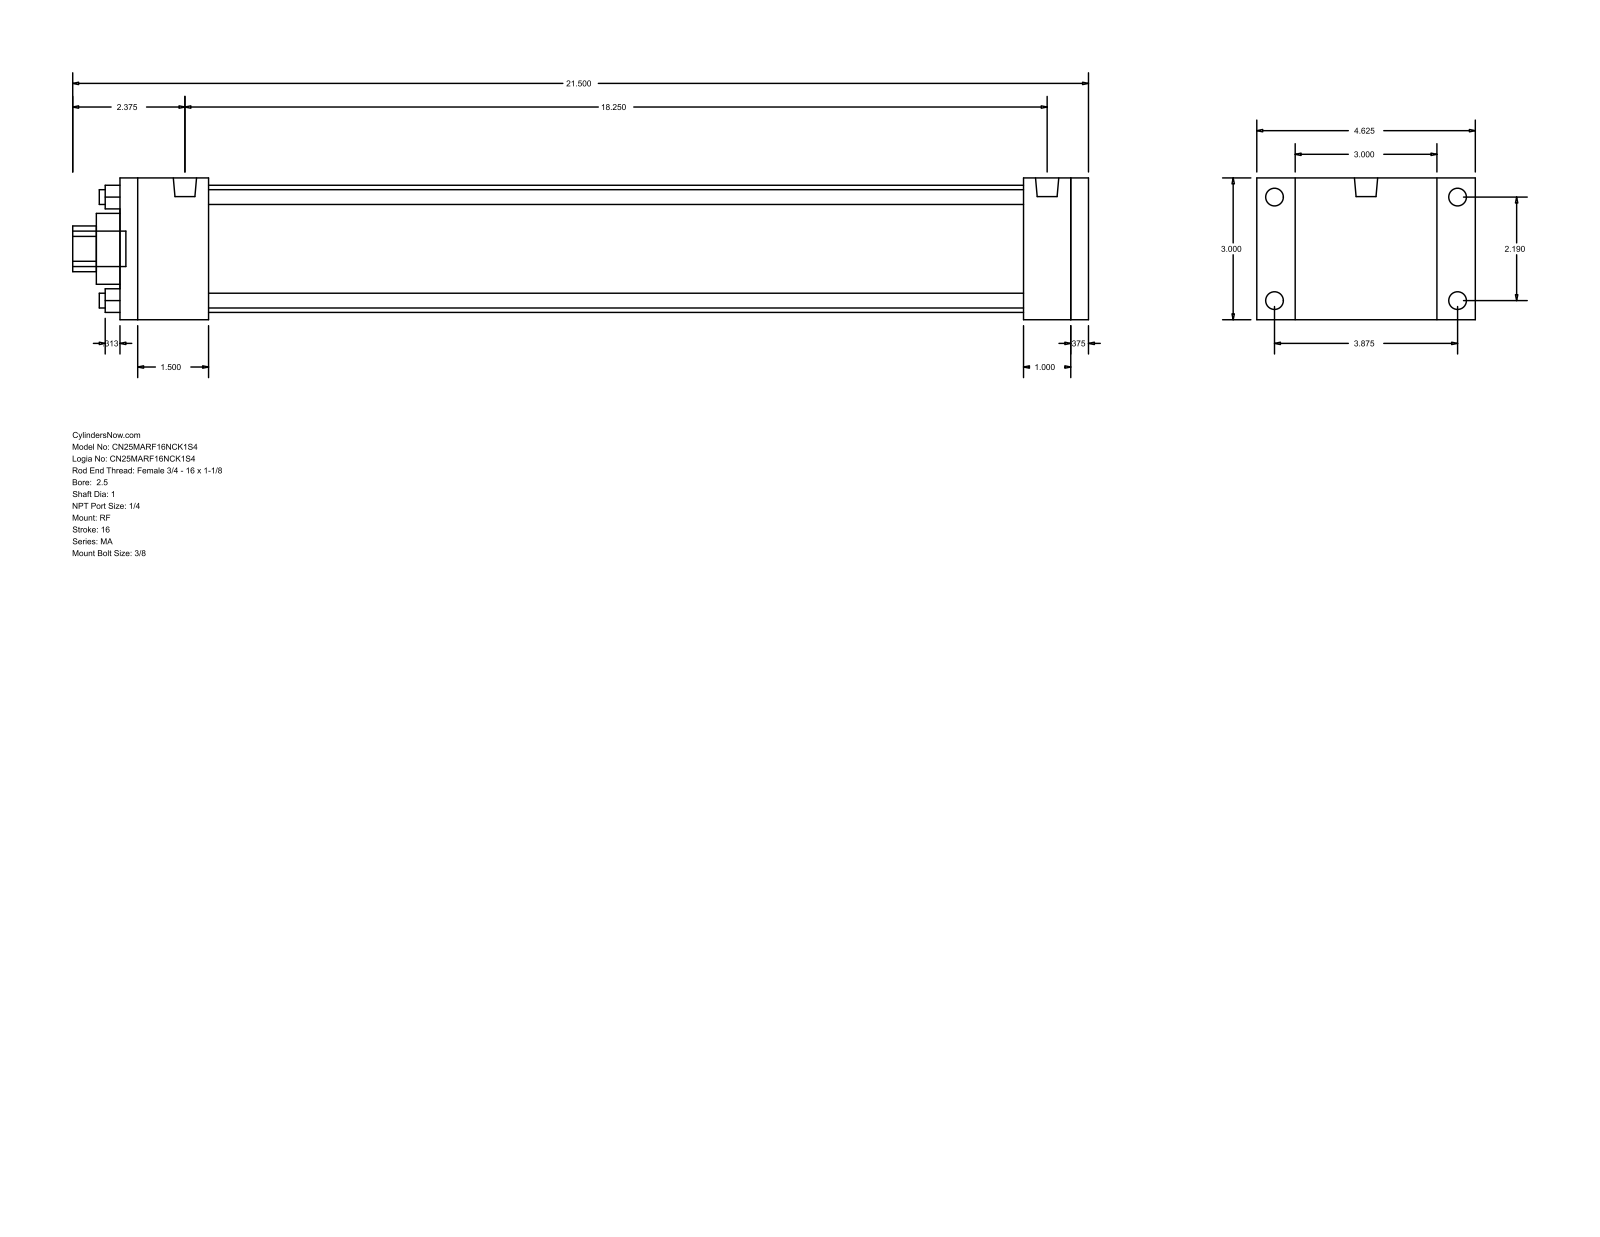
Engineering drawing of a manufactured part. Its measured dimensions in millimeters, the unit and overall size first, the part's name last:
Units: millimetres
Overall size (bounding box): 546.1 × 117.47 × 76.2
Round holes (diameter × count): ⌀7.94 ×4, ⌀25.4 ×1, ⌀38.1 ×1, ⌀68.33 ×1
Round bosses / shafts (diameter × count): ⌀9.53 ×4, ⌀7.94 ×4, ⌀12.49 ×2, ⌀19.05 ×1
Partial cylindrical surfaces — rounded edges, fillets, slot ends (radius × count): R12.29 ×1
Main face-to-face distances: 76.2, 520.7, 511.18, 9.52, 25.4, 47.63, 485.78, 438.15, 463.55, 473.07
Hole centre spacings: 39.33, 55.62, 78.66
Bodies: 0 solids, 92 faces (64 planar, 28 cylindrical, 0 other)
Part name (STEP PRODUCT): MA_RF__0250_1
STEP written by: GSSL Pune (CONFIG_CONTROL_DESIGN)
